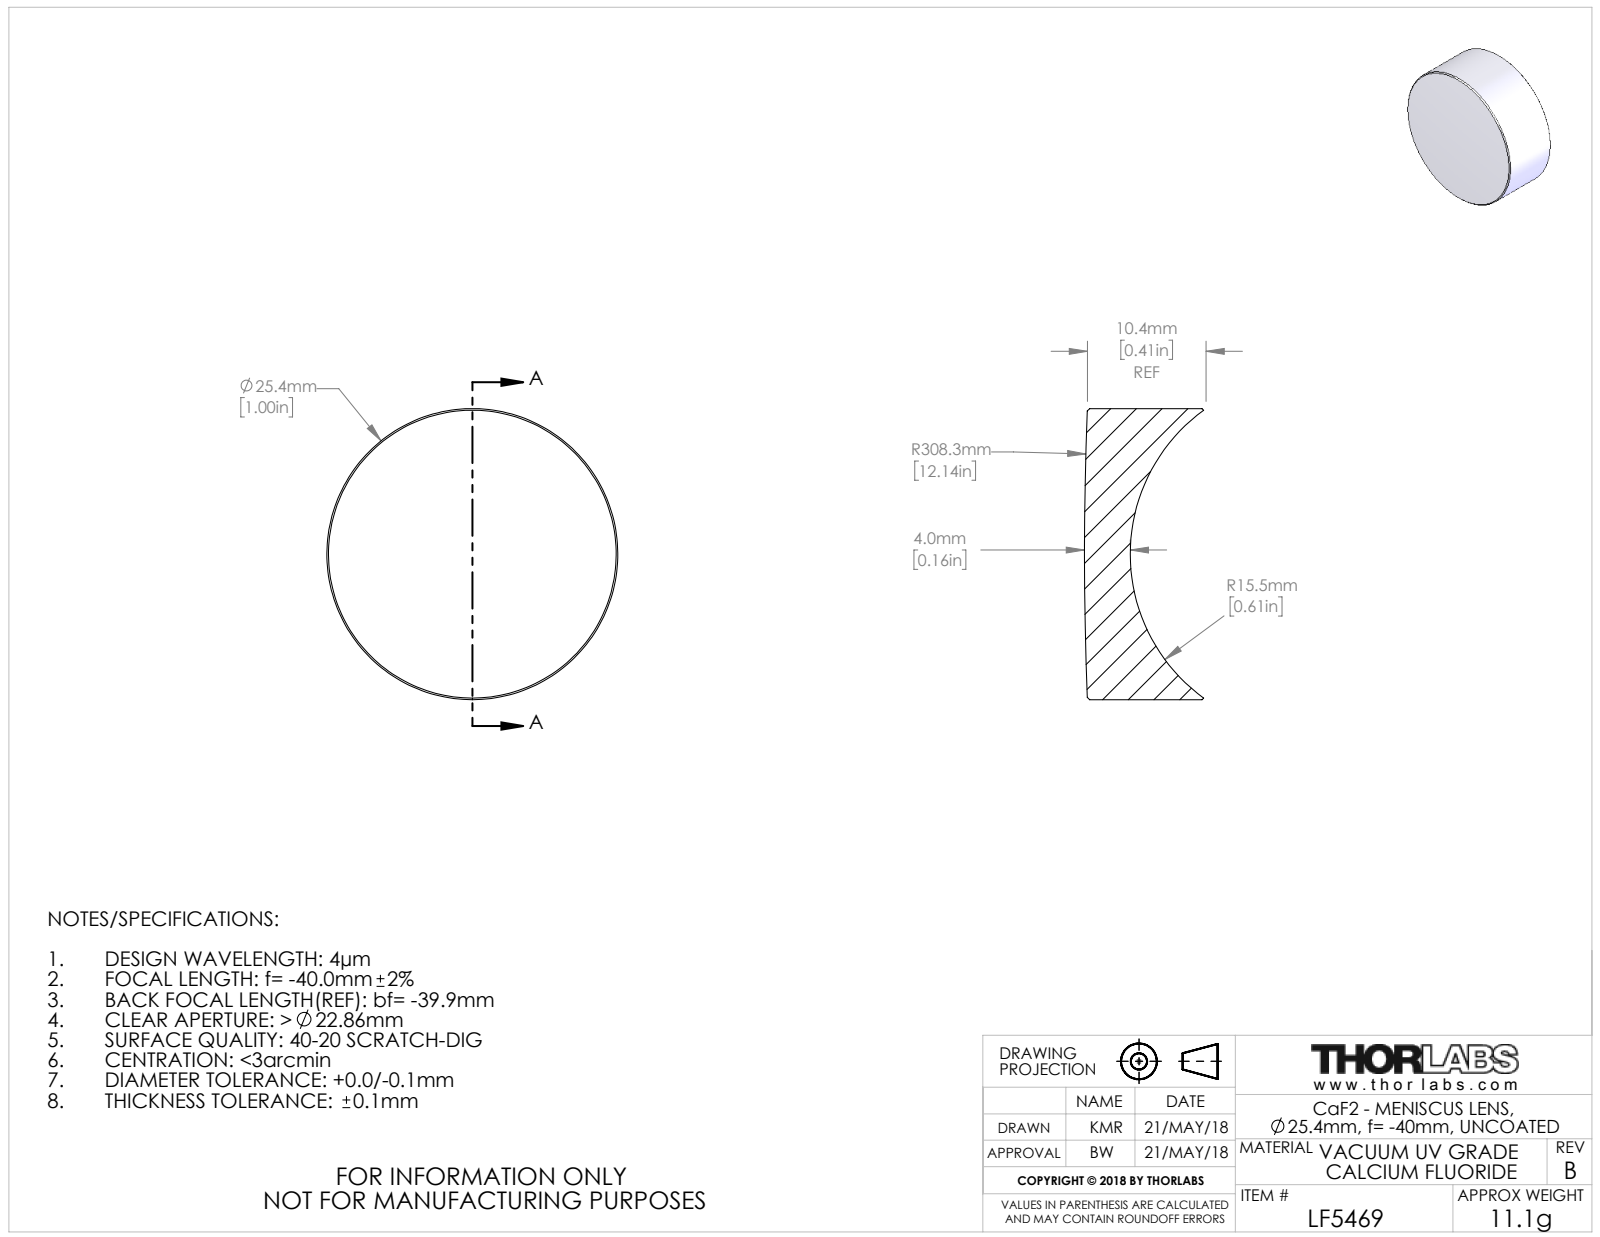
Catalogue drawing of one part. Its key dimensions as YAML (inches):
part_name: "21998-E0W"
step_written_by: "SolidWorks 2016 (CONFIG_CONTROL_DESIGN)"
units: inches
bodies: {solids: 1, faces: 10, planar: 0, cylindrical: 2, other: 8}
overall_size: [1, 1, 0.41]
volume: 0.212
surface_area: 3.003
round_bosses_or_shafts:
  - {diameter: 1, count: 1}
